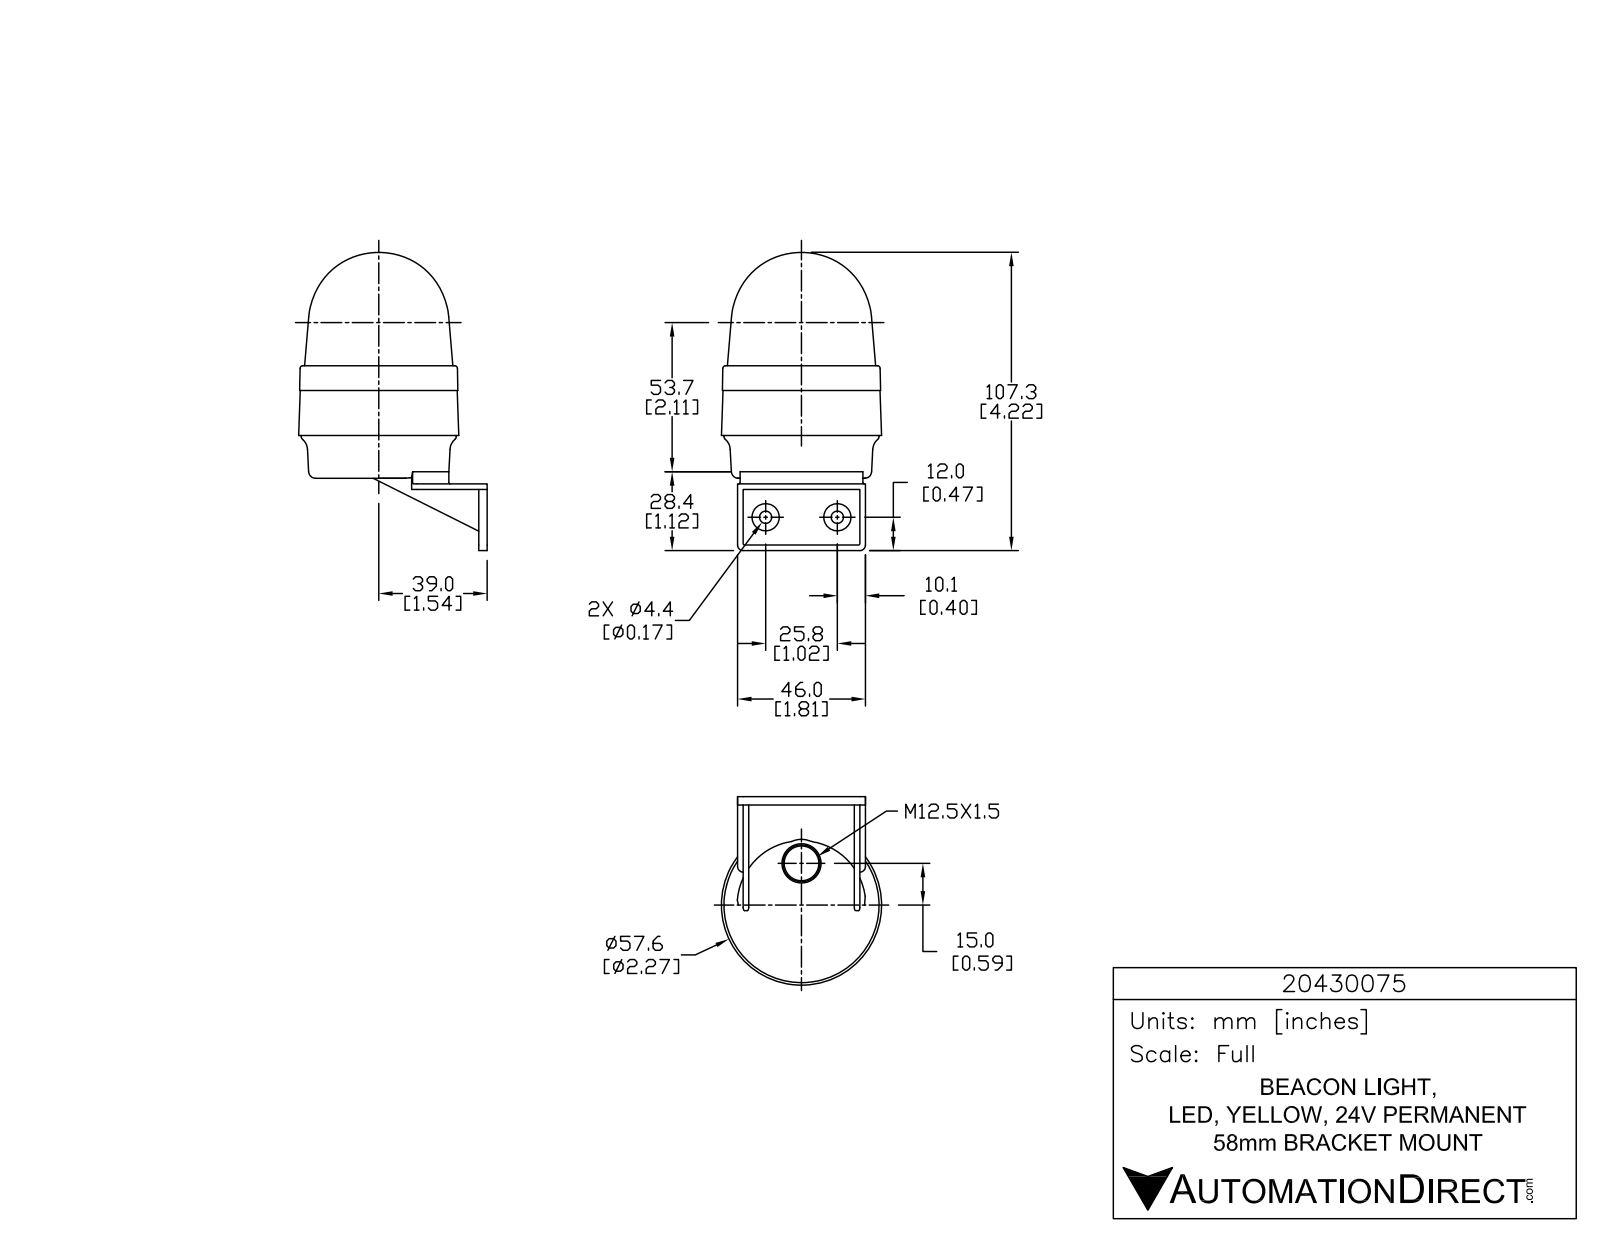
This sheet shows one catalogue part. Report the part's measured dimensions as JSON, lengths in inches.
{"part_name": "20430075", "step_written_by": "SolidWorks 2015 (AUTOMOTIVE_DESIGN)", "units": "inches", "bodies": {"solids": 1, "faces": 828, "planar": 551, "cylindrical": 179, "other": 98}, "overall_size": [4.225, 2.852, 2.407], "volume_in3": 10.27, "surface_area_in2": 33.38, "round_holes": [[0.039, 3], [0.173, 2]], "round_bosses_or_shafts": [[0.226, 3], [0.056, 3], [0.386, 2], [2.197, 1]], "partial_cylinders_radius": [[0.008, 6], [0.008, 6], [0.008, 6], [0.02, 6], [0.131, 6], [0.079, 4], [0.004, 3], [0.005, 3]], "face_to_face_distances": [0.079, 0.157, 1.575, 1.654, 0.039, 0.118, 1.496, 0.866, 0.945, 0.764], "hole_center_spacings": [1.016]}
